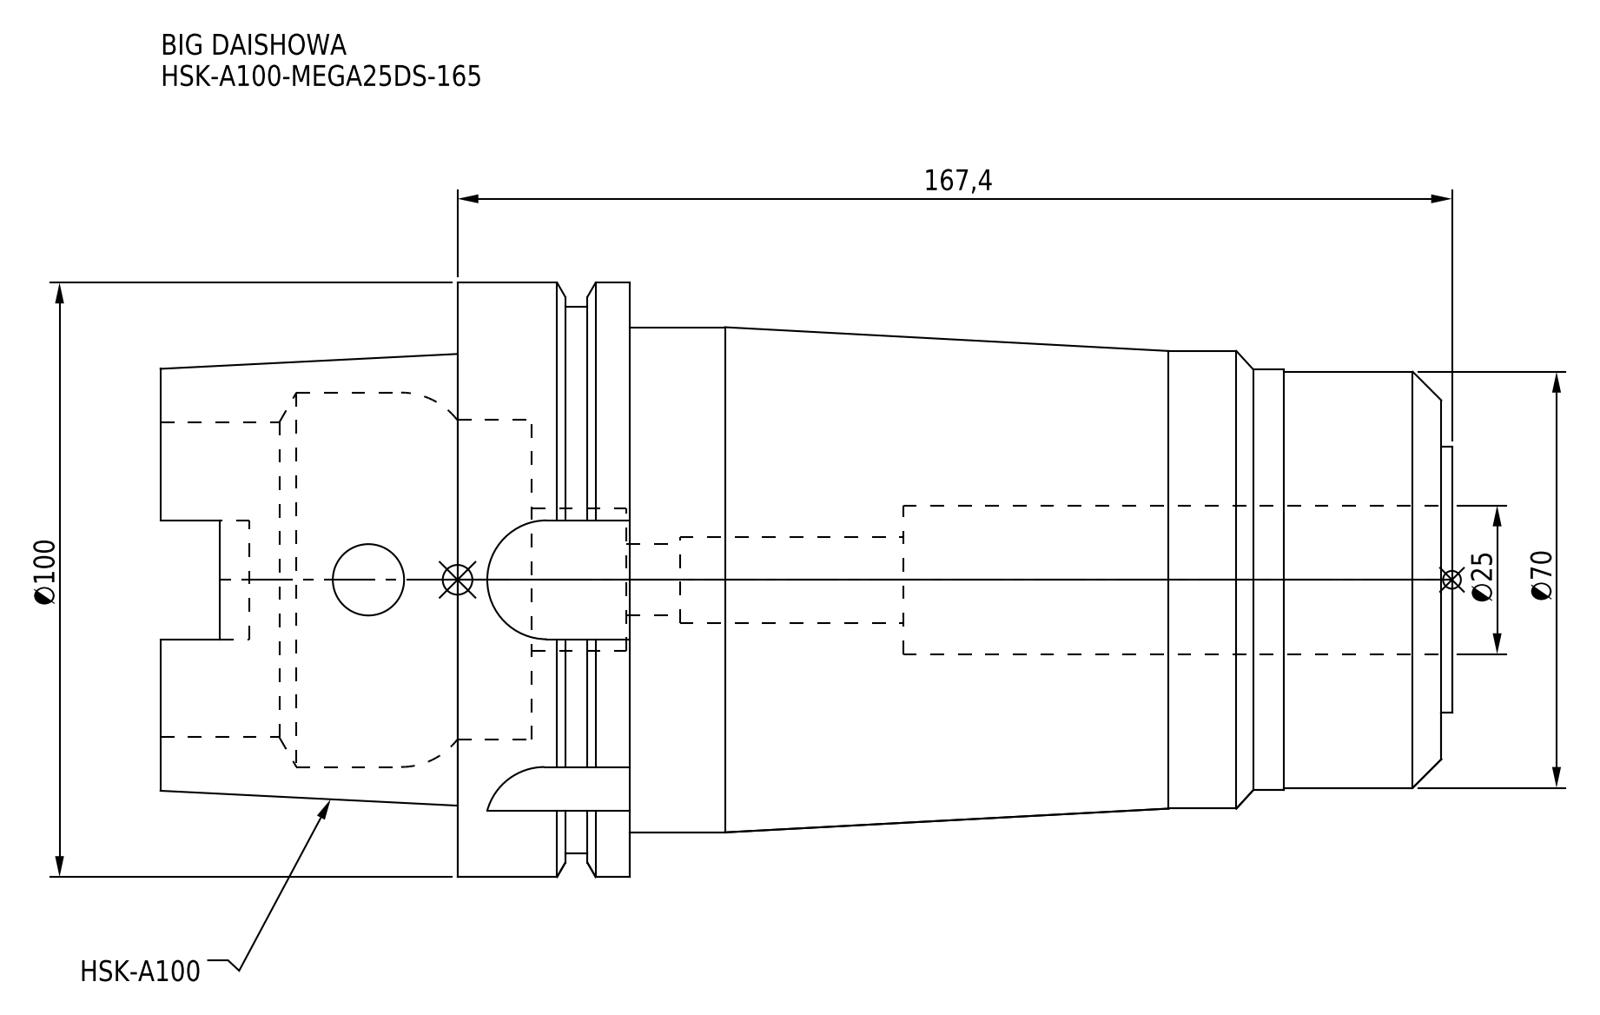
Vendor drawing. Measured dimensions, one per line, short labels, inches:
name: HSK-A100-MEGA25DS-165
written by: CREO PARAMETRIC BY PTC INC, 2016380 (AUTOMOTIVE_DESIGN)
unit: in
bodies: 1 solid, 102 faces (36 planar, 46 cylindrical, 20 other)
size: 8.559 × 3.937 × 3.937
volume: 52.78 in³; area: 141 in²
holes: 2× ⌀0.472, 1× ⌀0.571, 1× ⌀0.945, 1× ⌀0.984, 1× ⌀2.087, 1× ⌀2.118, 1× ⌀2.48
bosses: 1× ⌀3.937, 1× ⌀3.622, 1× ⌀3.346, 1× ⌀3.031, 1× ⌀2.783, 1× ⌀2.756, 1× ⌀1.764
rounds: 4× R0.192, 4× R0.394
face distances: 1.142, 0.652, 0.49, 5.378, 6.03, 6.52, 0.071, 5.449, 6.1, 6.591
